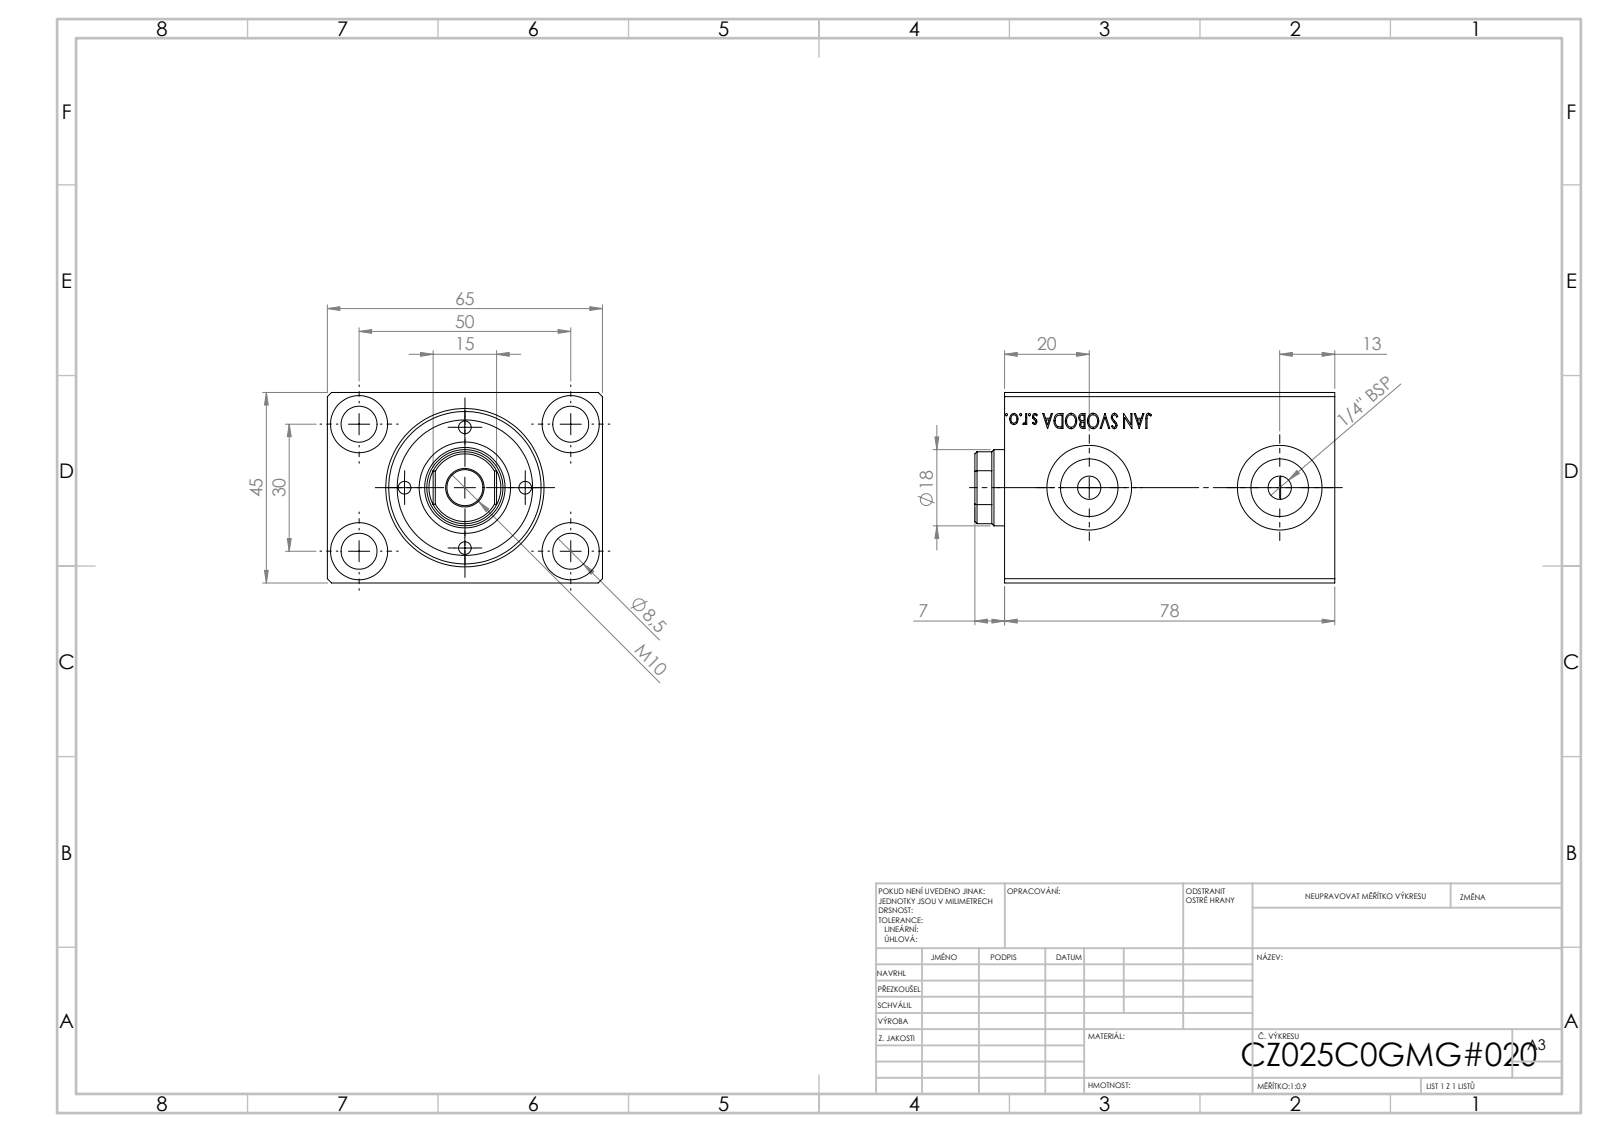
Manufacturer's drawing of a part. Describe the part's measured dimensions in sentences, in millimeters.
Its 3-D file was written by "SolidWorks 2019 (CONFIG_CONTROL_DESIGN)". It is 1 solid with 824 faces: 396 planar, 46 cylindrical and 382 other. Overall it measures 78 by 65 by 45 millimeters. Its volume is 162 949 cubic millimeters and its surface area 38 807 square millimeters. Round holes: 4 of diameter 8.5, 4 of diameter 13.5, 2 of diameter 5.5, 2 of diameter 8, 2 of diameter 13.6, 2 of diameter 20, 1 of diameter 25, 1 of diameter 36. The main face-to-face distances are 45, 65, 78, 77.8, 10.33, 67.67, 7, 70.8, 71, 65.2. The hole center spacings are 29.15, 30, 50, 58.31, 25, 45.
